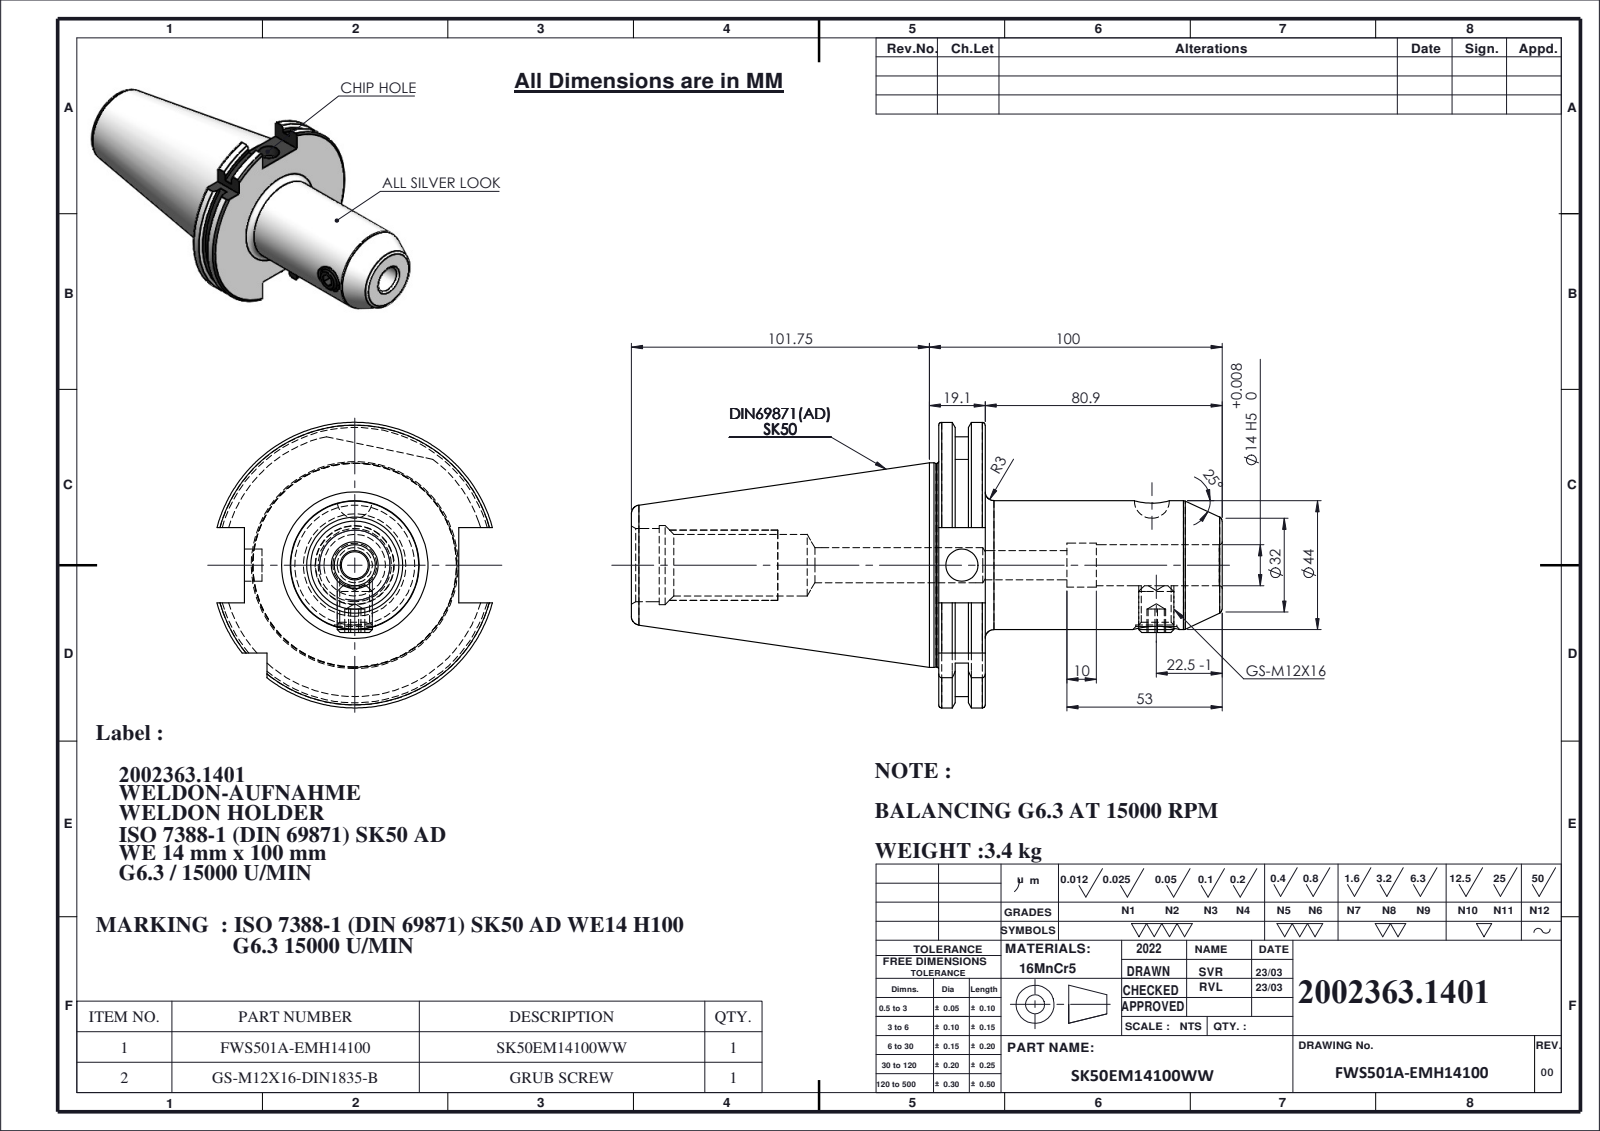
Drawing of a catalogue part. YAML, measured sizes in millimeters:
part_name: "SK50EM14100WW; 91506-WE114100; GS-M12X16-DIN1835-B"
step_written_by: "SolidWorks 2018 (CONFIG_CONTROL_DESIGN)"
units: millimeters
bodies: {solids: 2, faces: 139, planar: 39, cylindrical: 41, other: 59}
overall_size: [201.75, 97.5, 94.05]
volume: 440179
surface_area: 57465
round_holes:
  - {diameter: 14, count: 2}
  - {diameter: 10, count: 1}
  - {diameter: 10.2, count: 1}
  - {diameter: 11, count: 1}
  - {diameter: 12, count: 1}
  - {diameter: 15, count: 1}
  - {diameter: 21, count: 1}
  - {diameter: 25, count: 1}
  - {diameter: 27, count: 1}
round_bosses_or_shafts:
  - {diameter: 69.85, count: 1}
  - {diameter: 69.45, count: 1}
  - {diameter: 44, count: 1}
  - {diameter: 12, count: 1}
partial_cylinders:
  - {radius: 44.9, count: 1}
  - {radius: 48.75, count: 1}
face_to_face_distances: [15.9, 5.65, 10.25, 10.14, 4.49, 5.76, 96.8, 91.15, 86.66, 80.9]
